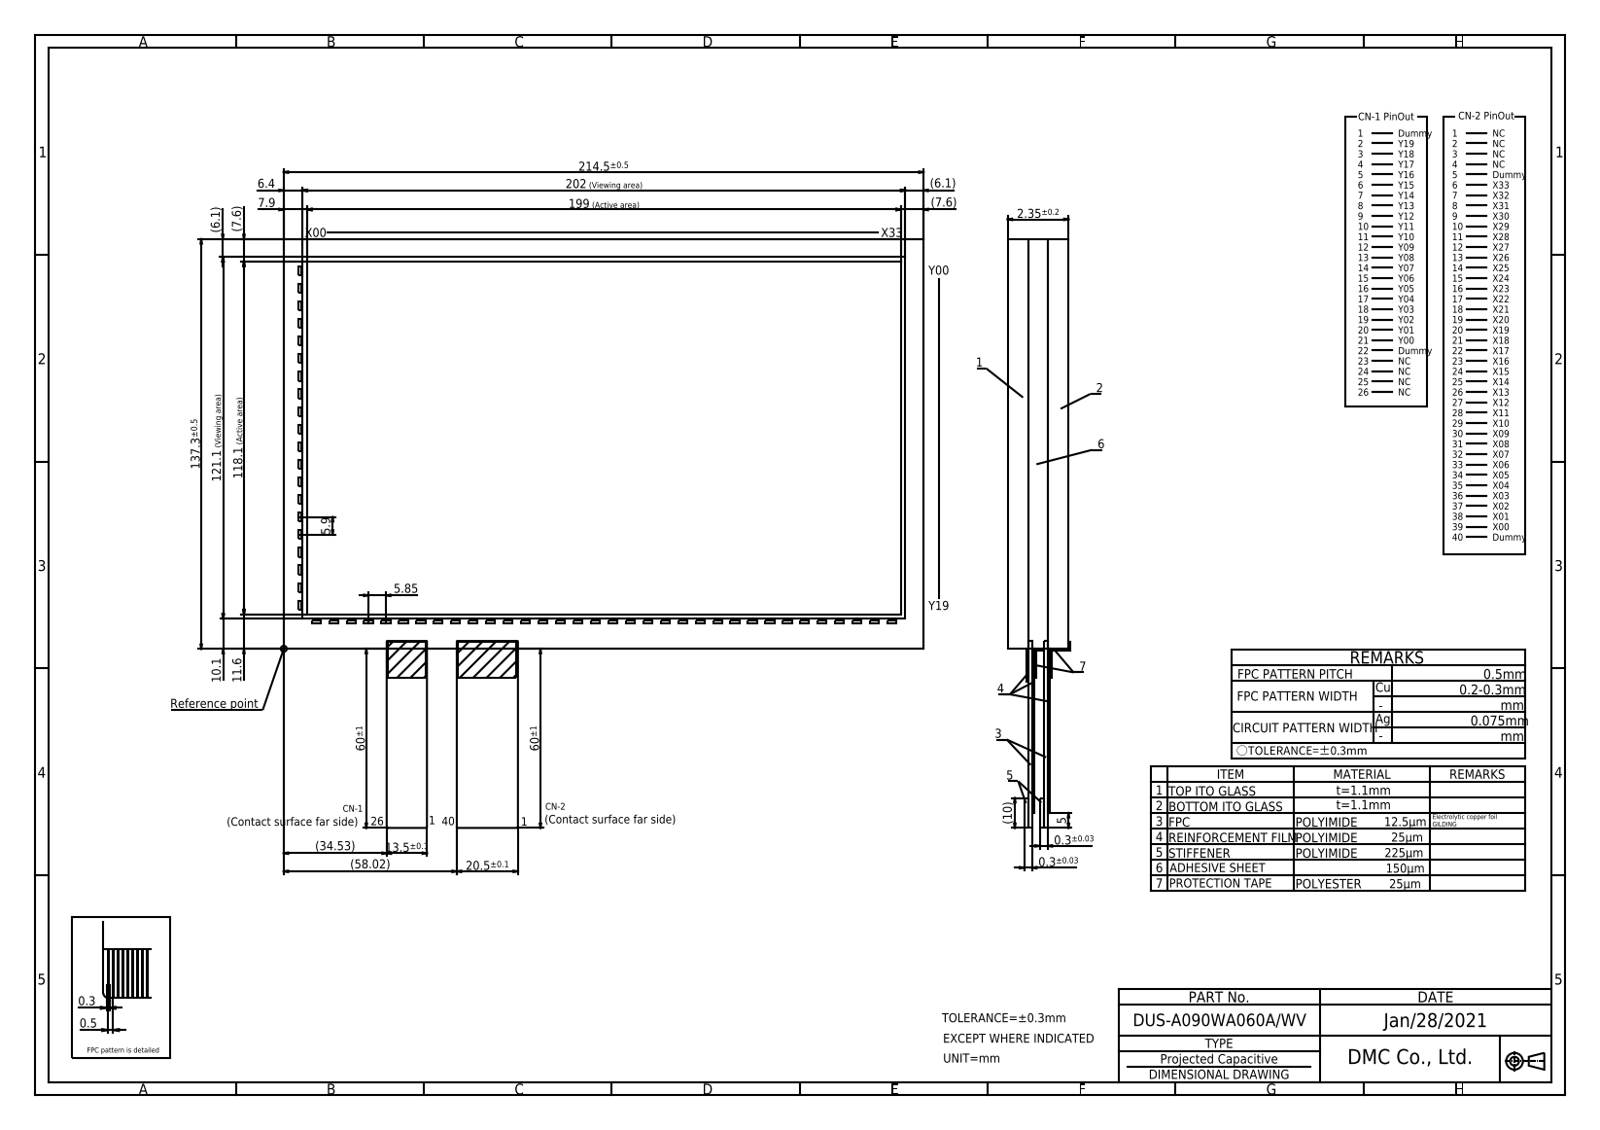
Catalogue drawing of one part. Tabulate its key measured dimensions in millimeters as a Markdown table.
| quantity | value |
| --- | --- |
| part name | DUS-A090WA060A／WV |
| STEP written by | Autodesk Inventor 2020 (CONFIG_CONTROL_DESIGN) |
| units | millimeters |
| bodies | 1 solid, 302 faces (298 planar, 4 cylindrical, 0 other) |
| overall size | 300.3 × 224.76 × 2.35 |
| volume | 69 422 mm³ |
| surface area | 64 826 mm² |
| partial cylindrical surfaces (radius × count) | 0.2 × 4 |
| main face-to-face distances | 2.35, 1.14, 1.21, 1.25, 1.1, 1.11, 1, 2.25, 137.3, 0.8 |
